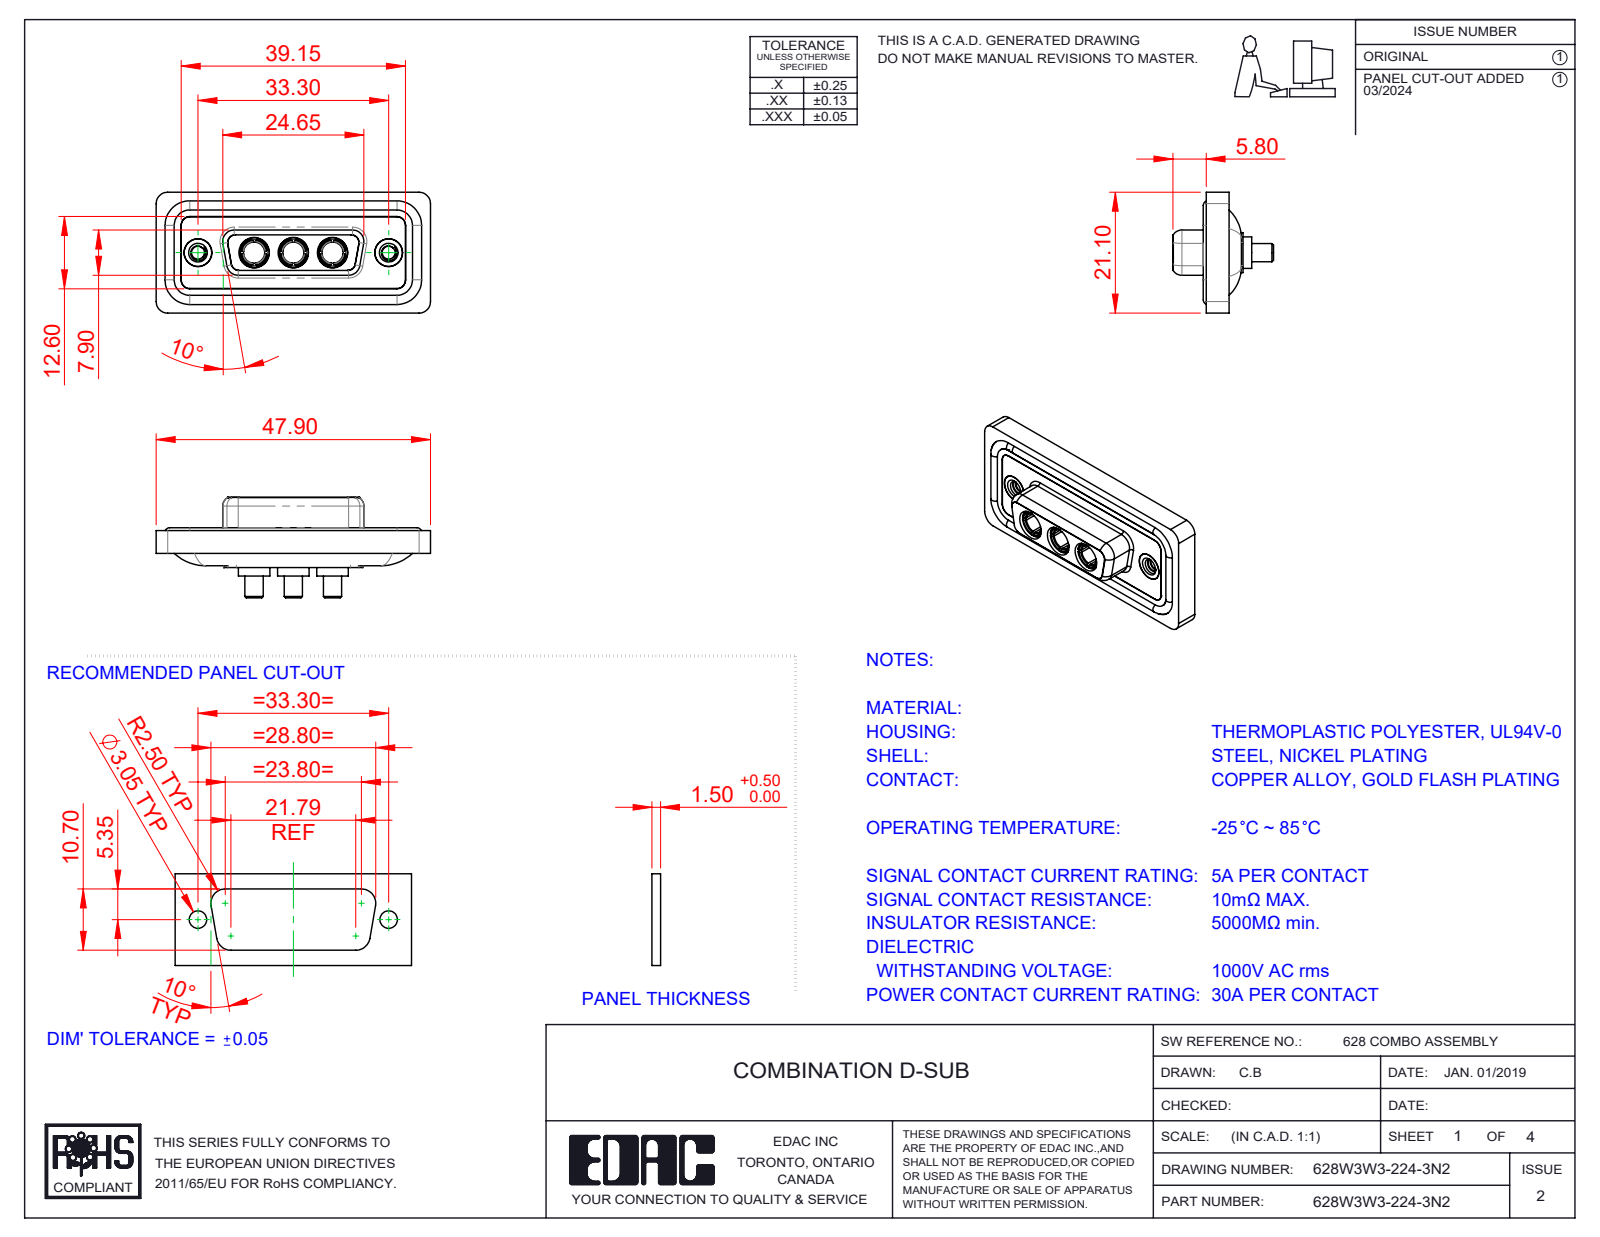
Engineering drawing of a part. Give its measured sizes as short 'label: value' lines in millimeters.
name: 628Combo Shell Rear_15 Contacts; 628W3W3-224-3N2; 628Combo Shell Front_15 Contacts; 628Combo Housing_3W3 (+3 more)
written by: SolidWorks 2023 (CONFIG_CONTROL_DESIGN)
unit: mm
bodies: 13 solids, 608 faces (192 planar, 257 cylindrical, 159 other)
size: 47.9 × 21.1 × 17.55
volume: 6 048 mm³; area: 9 752 mm²
holes: 5× ⌀4.85, 3× ⌀3.7, 3× ⌀5.3, 2× ⌀2.26, 2× ⌀4, 2× ⌀4.05, 2× ⌀5
bosses: 4× ⌀1.6, 3× ⌀5.5, 3× ⌀5.2, 3× ⌀4.96, 3× ⌀4.75, 3× ⌀3.75, 3× ⌀3.2, 2× ⌀4.95
rounds: 22× R1.5, 20× R2, 12× R1.35, 8× R1.6, 4× R0.25, 4× R0.5, 4× R0.6, 4× R0.65
face distances: 0.4, 1.8, 1.6, 0.5, 7.45, 1.1, 2.9, 5.65, 7.05, 6.6
hole spacings: 6.85, 9.8, 16.65, 23.5, 13.7, 33.3
